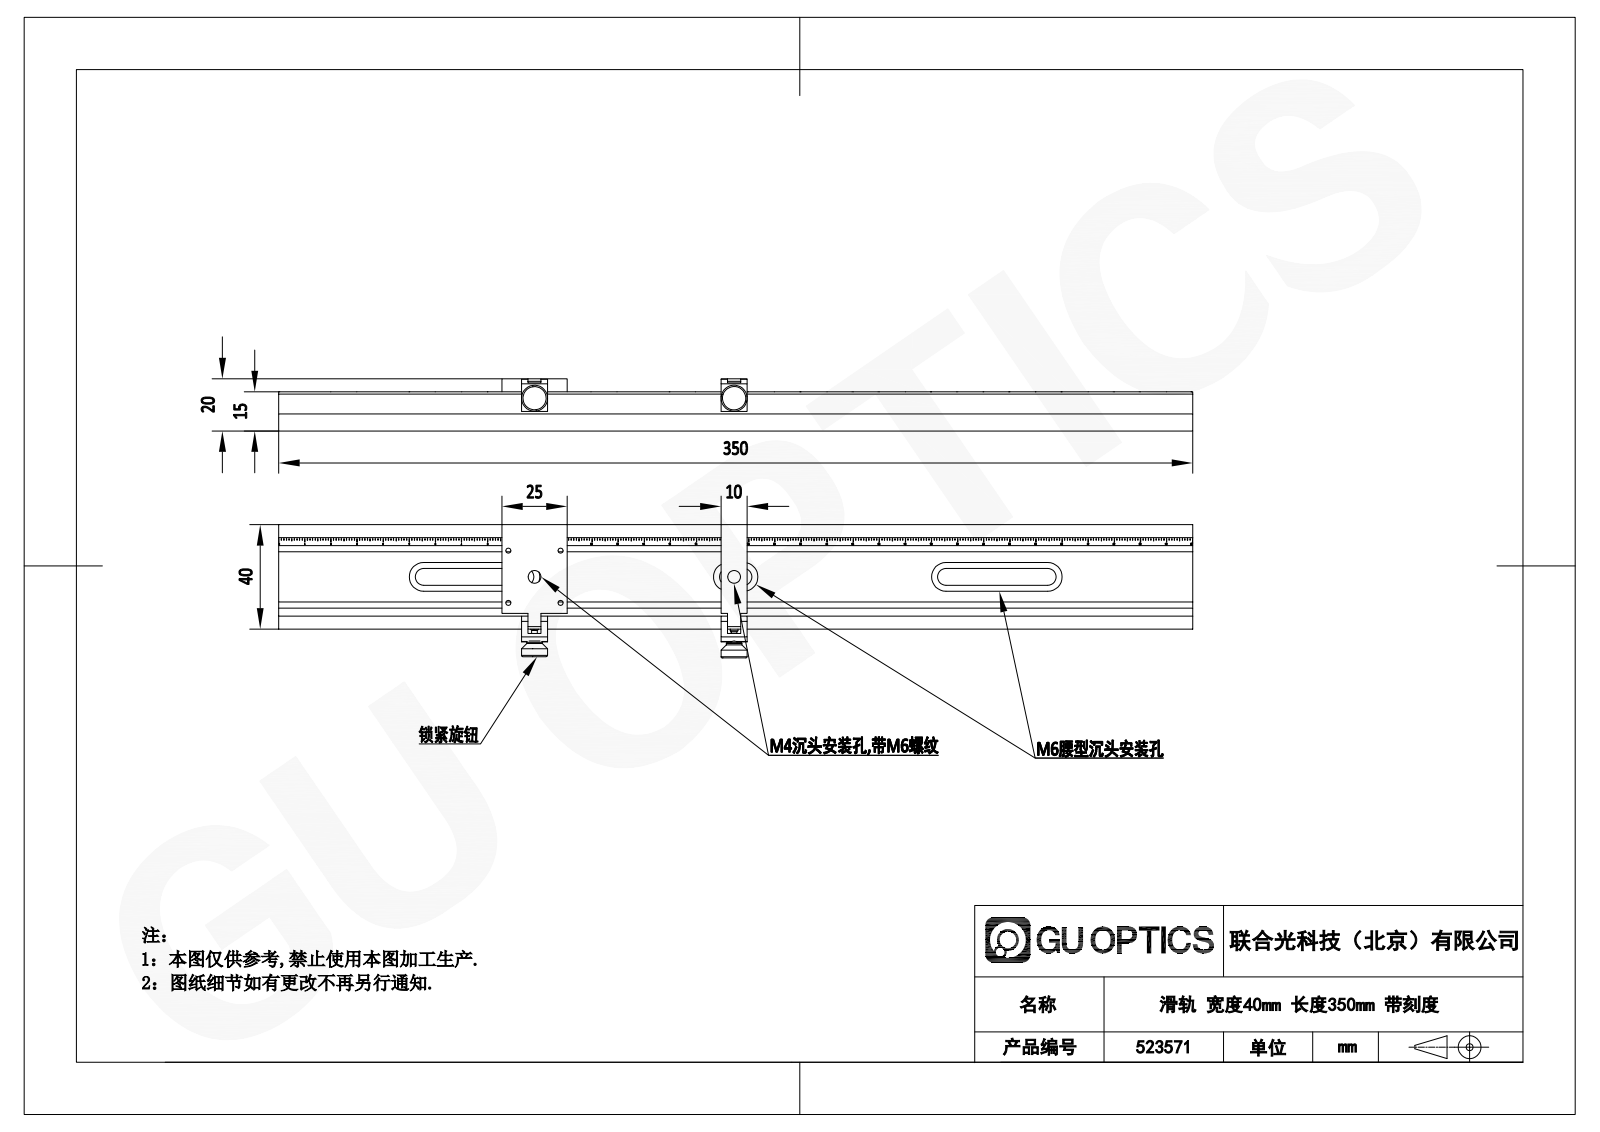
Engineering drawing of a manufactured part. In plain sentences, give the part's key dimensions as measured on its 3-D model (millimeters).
The part is named "523571". Its 3-D file was written by "SolidWorks 2020 (CONFIG_CONTROL_DESIGN)". It is 8 solids with 3355 faces: 2601 planar, 83 cylindrical and 671 other. Overall it measures 350 by 51.03 by 20 millimeters. Its volume is 137 249 cubic millimeters and its surface area 52 985 square millimeters. Round holes: 4 of diameter 2.05, 2 of diameter 2.5, 2 of diameter 3.2, 2 of diameter 5, 2 of diameter 8, 1 of diameter 1.5, 1 of diameter 2. Round bosses or shafts: 2 of diameter 10, 2 of diameter 6, 2 of diameter 3, 2 of diameter 2.2. Partial cylindrical surfaces (rounded edges, fillets, slot ends): 6 of radius 3.25, 6 of radius 5.5, 1 of radius 1.25, 1 of radius 2.5, 1 of radius 4.5, 1 of radius 12.5. The main face-to-face distances are 6, 14.5, 0.5, 6.5, 15, 8.5, 5, 40, 8, 14. The hole center spacings are 14.14, 20, 28.28, 67.16, 76.41, 86.99.
